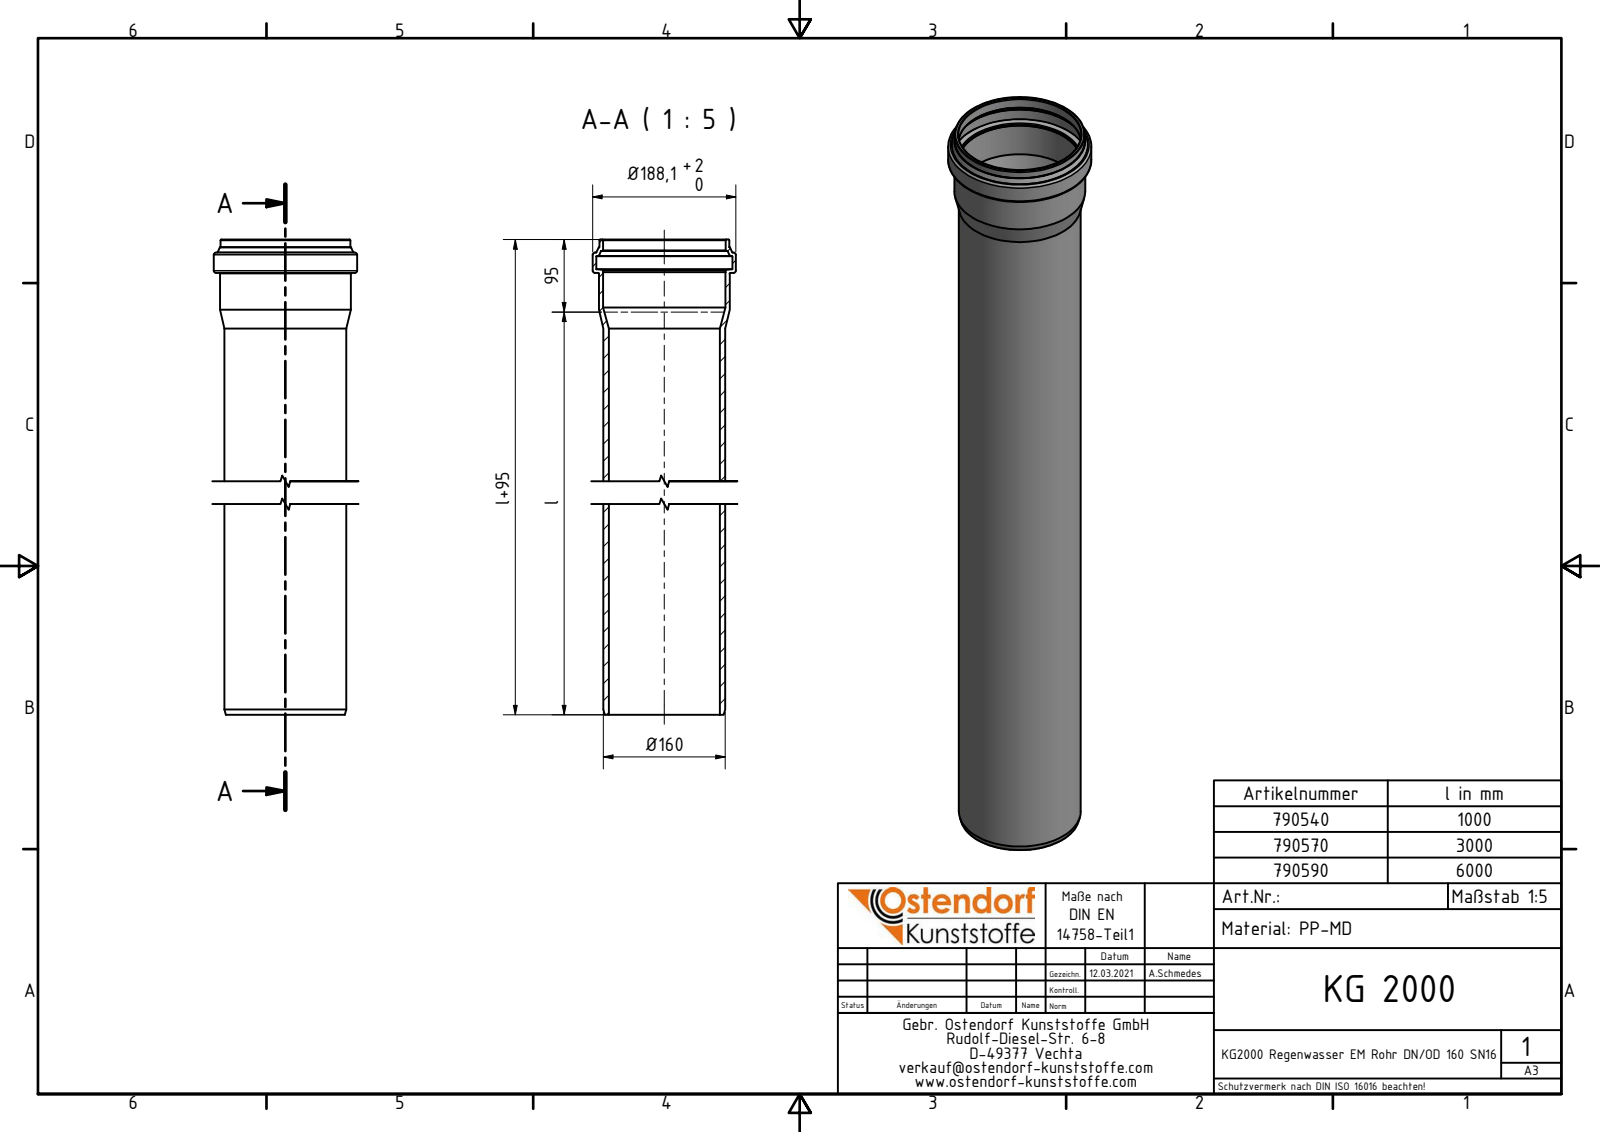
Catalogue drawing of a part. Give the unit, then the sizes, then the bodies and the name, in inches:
Units: inches
Overall size (bounding box): 239.961 × 7.406 × 7.406
Round holes (diameter × count): ⌀5.74 ×1, ⌀6.323 ×1, ⌀6.339 ×1, ⌀7.035 ×1
Round bosses / shafts (diameter × count): ⌀7.406 ×1, ⌀6.764 ×1, ⌀6.709 ×1, ⌀6.299 ×1
Main face-to-face distances: 238.24, 239.961, 1.72, 239.291, 1.051, 0.669, 239.563, 1.323, 0.272, 0.397
Volume: 1 267 in³ · Surface area: 9 123 in²
Bodies: 1 solid, 37 faces (6 planar, 9 cylindrical, 22 other)
Part name (STEP PRODUCT): 790590 KG2000EM Rohr-Passlängen Regenwasser DN160x6000 SN16
STEP written by: Autodesk Inventor 2020 (AUTOMOTIVE_DESIGN)
